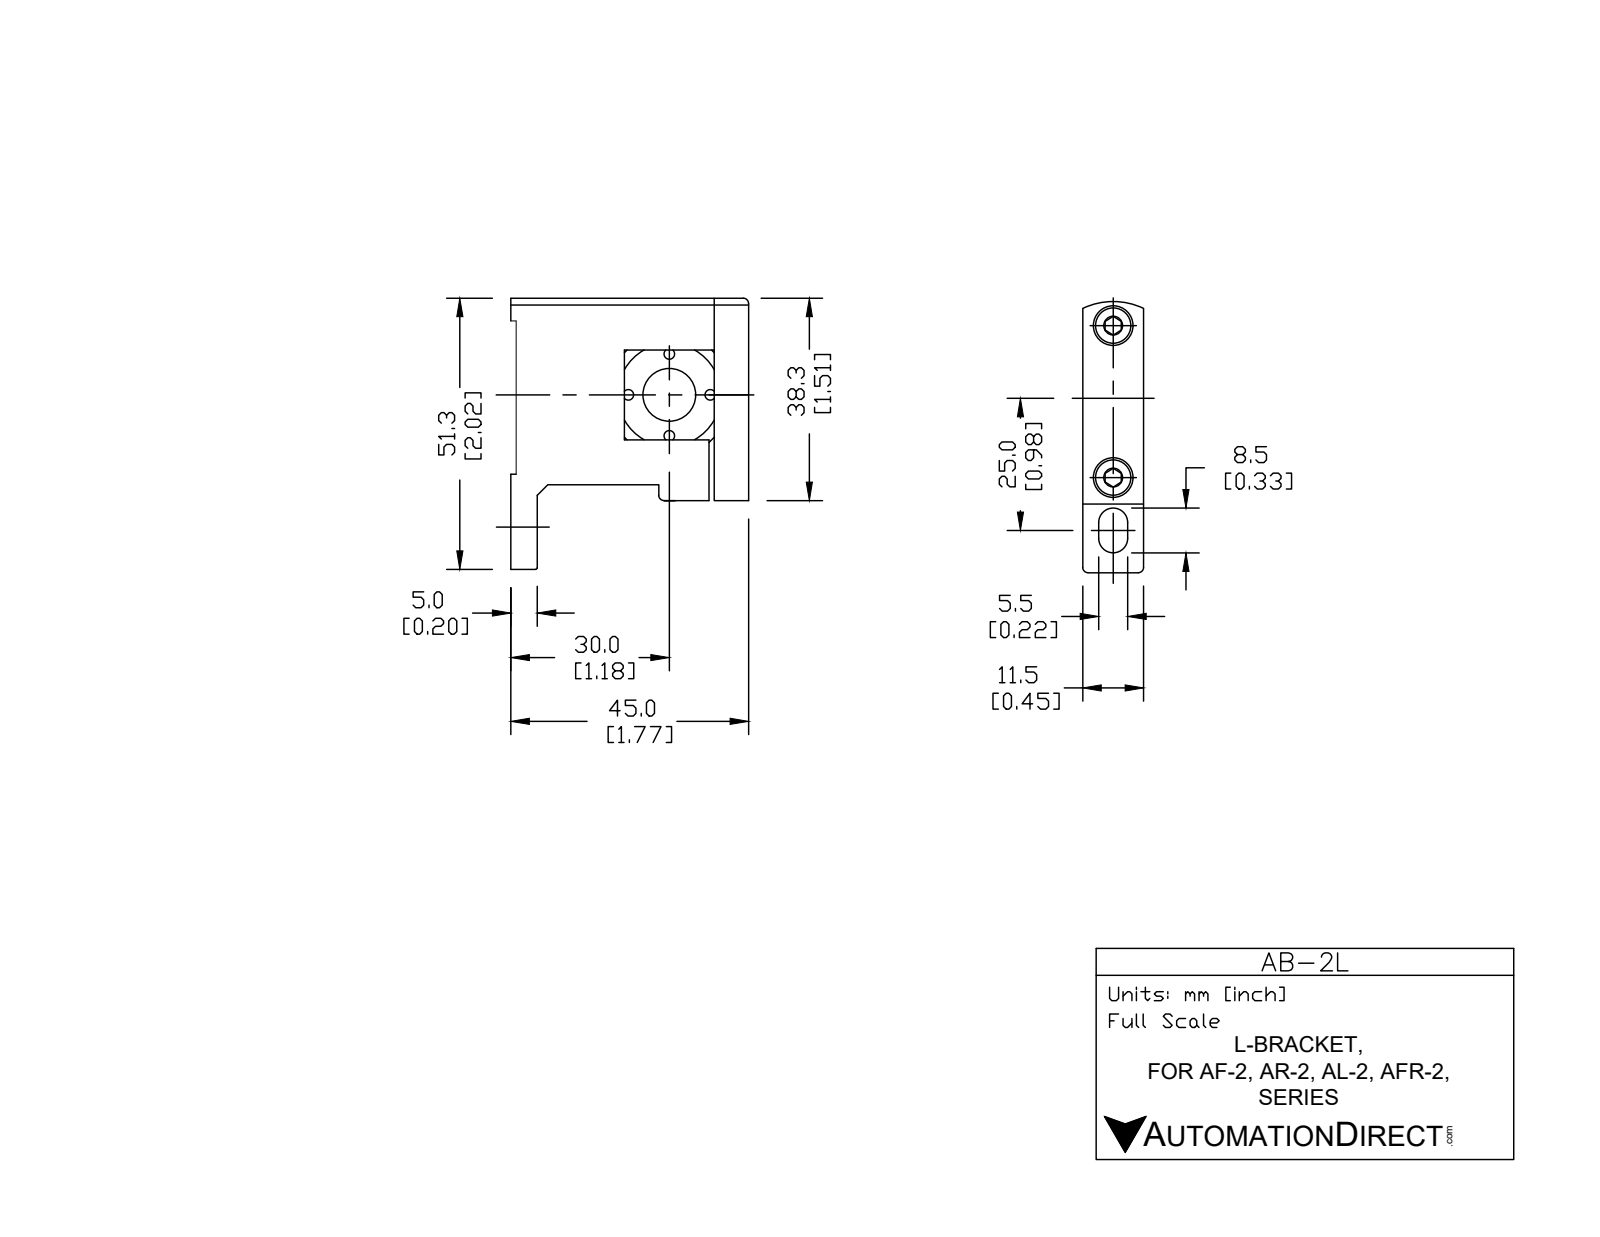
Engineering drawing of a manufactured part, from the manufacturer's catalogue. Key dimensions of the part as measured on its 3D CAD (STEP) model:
Part name (STEP PRODUCT): AB-2L
STEP written by: SolidWorks 2015 (CONFIG_CONTROL_DESIGN)
Units: millimetres
Bodies: 3 solids, 97 faces (63 planar, 22 cylindrical, 12 other)
Overall size (bounding box): 51.3 × 45 × 11.5
Volume: 15 351 mm³ · Surface area: 7 565 mm²
Round holes (diameter × count): ⌀4.5 ×2, ⌀6.21 ×2, ⌀10 ×1
Round bosses / shafts (diameter × count): ⌀5.75 ×2, ⌀4 ×2
Partial cylindrical surfaces — rounded edges, fillets, slot ends (radius × count): R2.75 ×2, R1.5 ×1, R13.37 ×1
Main face-to-face distances: 11.5, 20, 1.5, 43.75, 18.5, 3, 2, 5, 40, 6.5
Hole centre spacings: 28.75
